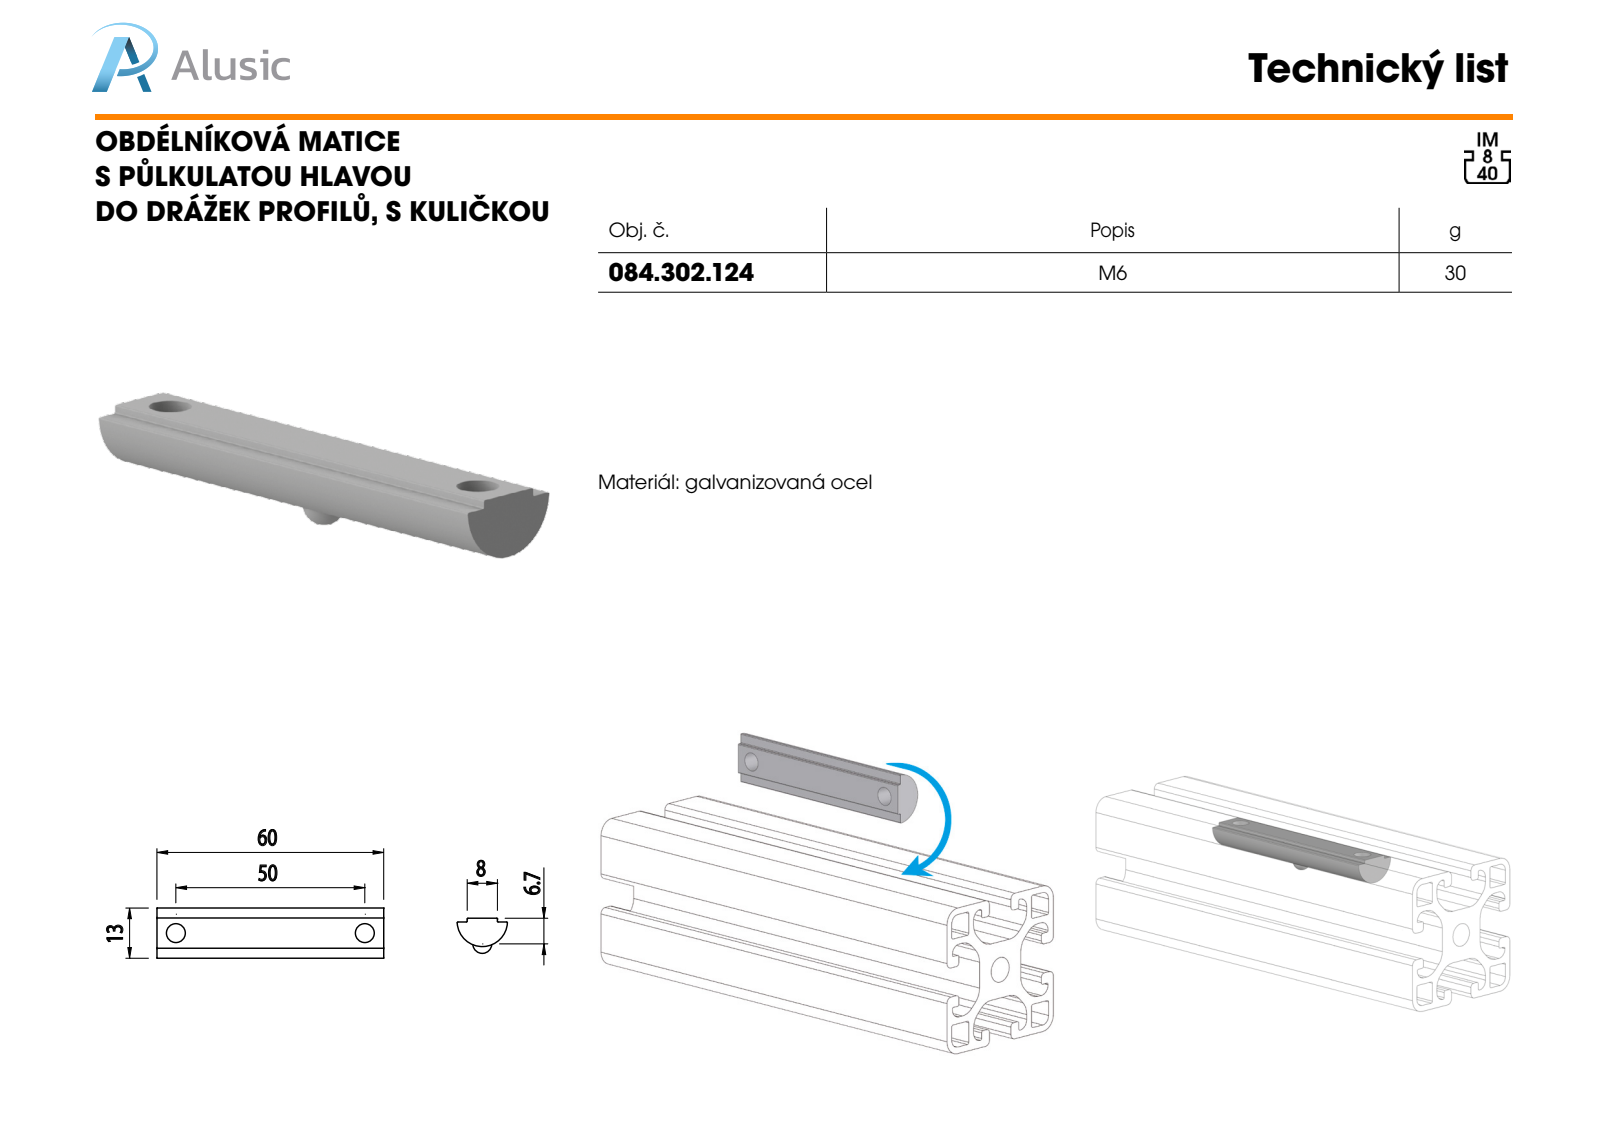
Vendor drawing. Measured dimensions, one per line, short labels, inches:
name: 084.302.124
written by: SolidWorks 2016 (CONFIG_CONTROL_DESIGN)
unit: in
bodies: 1 solid, 21 faces (7 planar, 12 cylindrical, 2 other)
size: 2.362 × 0.523 × 0.366
volume: 0.26 in³; area: 3.773 in²
holes: 2× ⌀0.197
rounds: 6× R0.008, 1× R0.262
face distances: 0.039, 2.362, 0.315
hole spacings: 1.969
